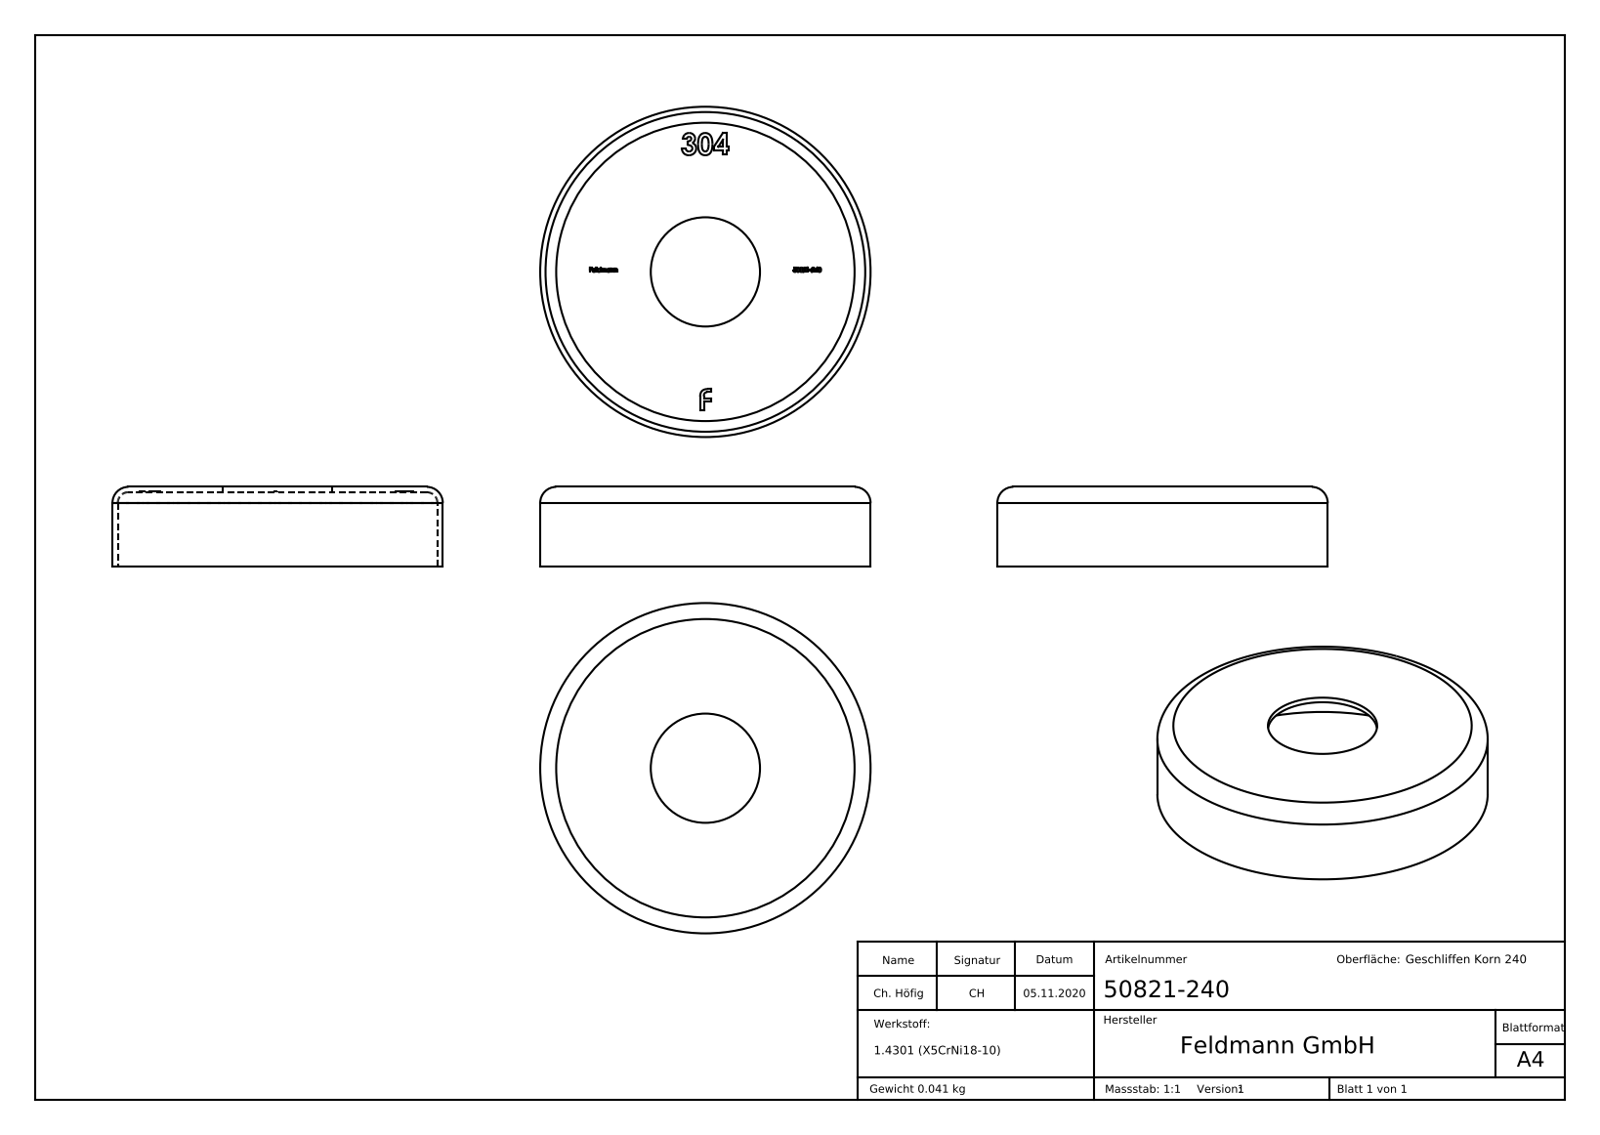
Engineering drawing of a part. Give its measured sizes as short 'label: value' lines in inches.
name: 50821-240
written by: SolidWorks 2018 (CONFIG_CONTROL_DESIGN)
unit: in
bodies: 1 solid, 294 faces (156 planar, 6 cylindrical, 132 other)
size: 2.441 × 2.441 × 0.591
volume: 0.315 in³; area: 16.43 in²
holes: 1× ⌀0.807, 1× ⌀2.362
bosses: 1× ⌀2.441
face distances: 0.039, 0.551, 0.591, 0.555, 0.035, 0.028, 0.197, 0.898, 0.169, 0.023
